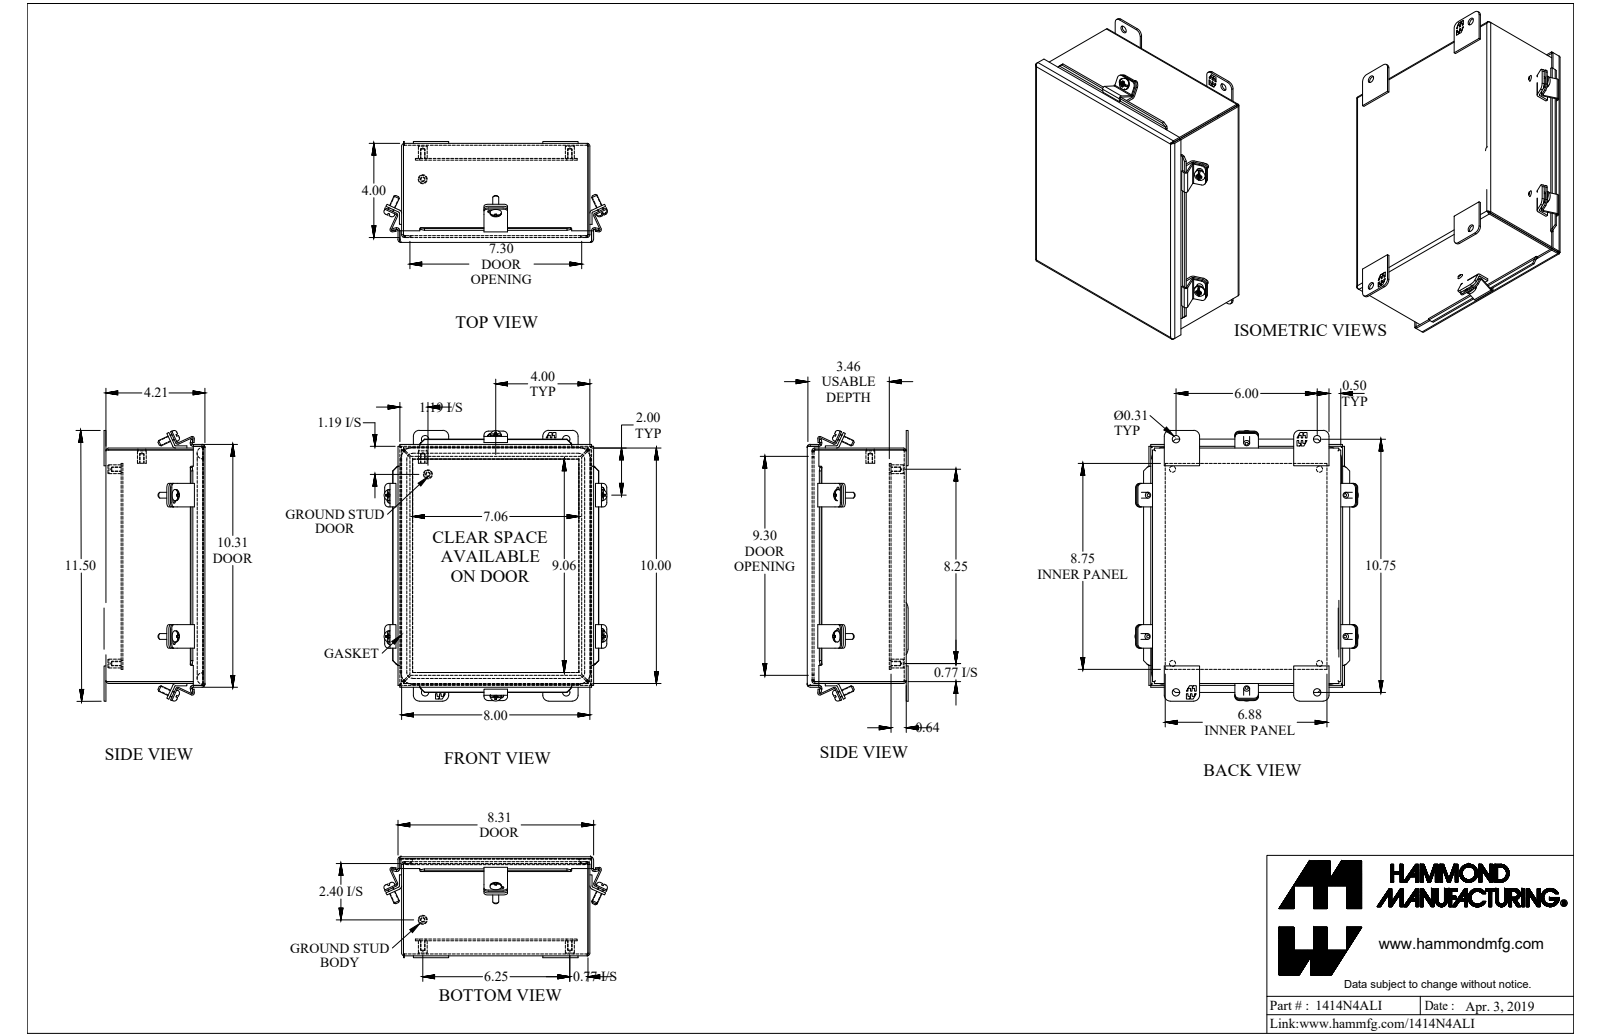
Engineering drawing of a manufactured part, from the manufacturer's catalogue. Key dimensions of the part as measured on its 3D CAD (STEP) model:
Part name (STEP PRODUCT): 1414N4ALI
STEP written by: SolidWorks 2018 (AUTOMOTIVE_DESIGN)
Units: inches
Bodies: 32 solids, 889 faces (609 planar, 200 cylindrical, 80 other)
Overall size (bounding box): 11.5 × 9.49 × 4.286
Volume: 37.14 in³ · Surface area: 945.3 in²
Round holes (diameter × count): ⌀0.159 ×6, ⌀0.213 ×6, ⌀0.265 ×4, ⌀0.313 ×4
Round bosses / shafts (diameter × count): ⌀0.48 ×6, ⌀0.375 ×6, ⌀0.33 ×6, ⌀0.25 ×6
Partial cylindrical surfaces — rounded edges, fillets, slot ends (radius × count): R0.188 ×16, R0.141 ×12, R0.25 ×12, R0.01 ×10, R0.029 ×8, R0.036 ×8, R0.048 ×8, R0.086 ×8
Main face-to-face distances: 0.081, 4.125, 4.206, 4.044, 7.919, 0.562, 0.643, 3.563, 3.482, 9.919
Hole centre spacings: 6, 6.25, 8.25, 10.35, 10.75, 12.311, 0.31, 1.231
